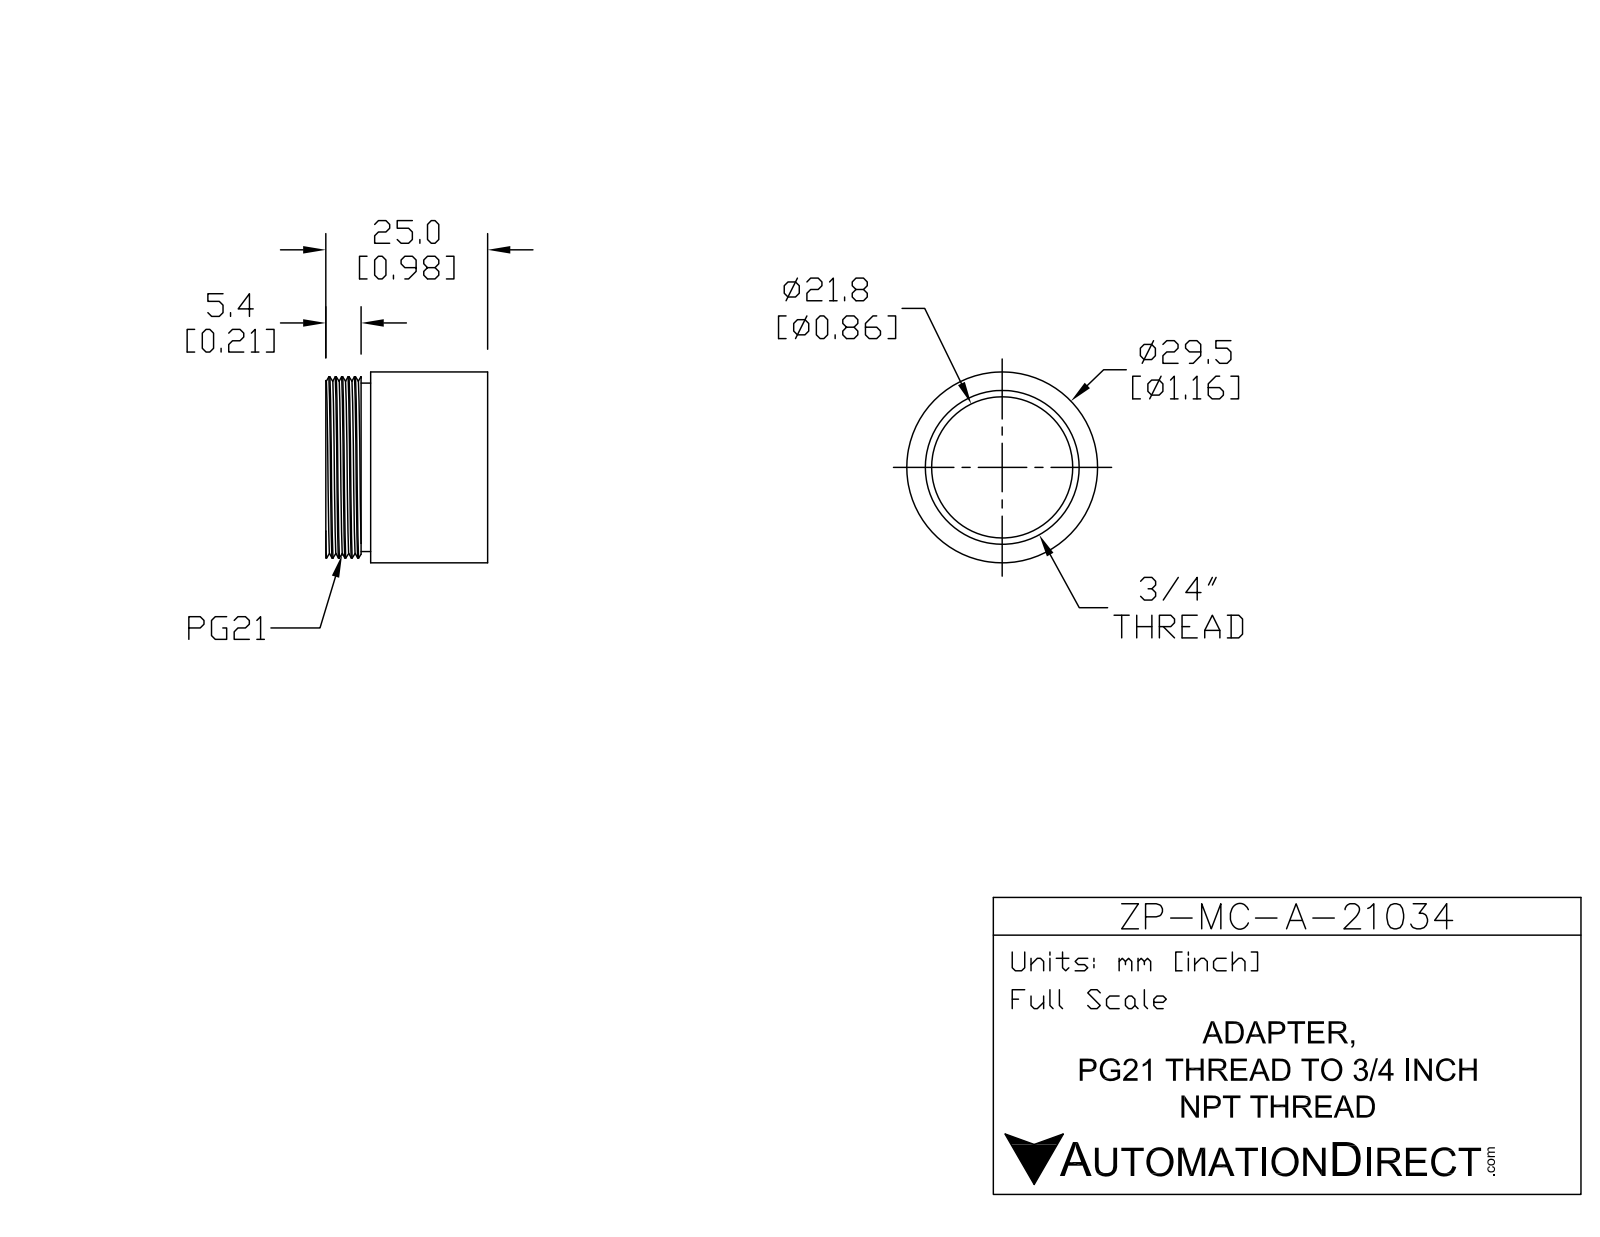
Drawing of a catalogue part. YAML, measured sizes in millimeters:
part_name: "ZP-MC-A-21034"
step_written_by: "SolidWorks 2011 (AUTOMOTIVE_DESIGN)"
units: millimeters
bodies: {solids: 1, faces: 27, planar: 6, cylindrical: 17, other: 4}
overall_size: [29.75, 29.75, 25]
volume: 5768
surface_area: 6066
round_holes:
  - {diameter: 22, count: 1}
  - {diameter: 24, count: 1}
round_bosses_or_shafts:
  - {diameter: 29.75, count: 1}
  - {diameter: 28.25, count: 1}
  - {diameter: 26.25, count: 1}
face_to_face_distances: [25, 7, 18, 10.5, 3.5, 14.5, 5.5, 1.5, 5, 19.5]
